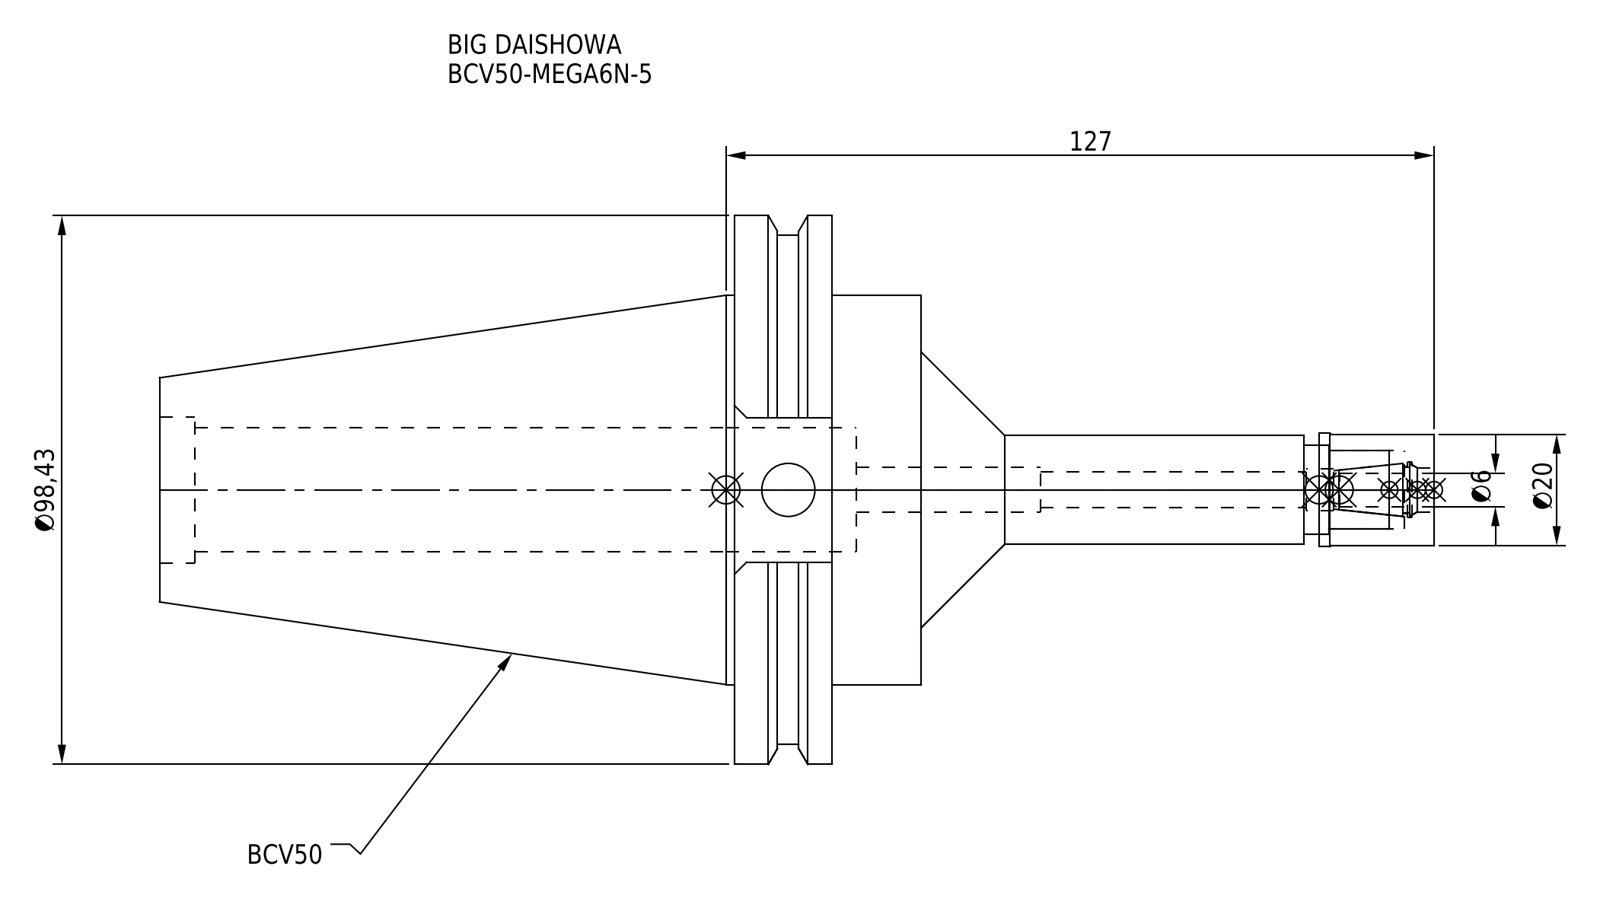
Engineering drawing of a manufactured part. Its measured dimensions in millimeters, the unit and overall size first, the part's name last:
Units: millimetres
Overall size (bounding box): 228.6 × 98.42 × 94.95
Round holes (diameter × count): ⌀6.4 ×1, ⌀7.5 ×1, ⌀7.9 ×1, ⌀8 ×1, ⌀8.5 ×1, ⌀9.53 ×1, ⌀10 ×1, ⌀14 ×1, ⌀16 ×1, ⌀22.3 ×1, ⌀26.23 ×1
Round bosses / shafts (diameter × count): ⌀98.42 ×1, ⌀91.29 ×1, ⌀69.85 ×1, ⌀20.3 ×1, ⌀20 ×1, ⌀19.5 ×1
Main face-to-face distances: 17.55, 15.95, 33.5, 136.6, 120.65, 103.1, 72.95, 11.6, 4.35, 21.9
Volume: 415 810 mm³ · Surface area: 58 369 mm²
Bodies: 2 solids, 91 faces (33 planar, 44 cylindrical, 14 other)
Part name (STEP PRODUCT): MGN6_1.stp; BCV50MN06050-060_ASM.stp; BCV50-MEGA6N-5-060-FreeParts; DXF_TEMP_ASSY_ASM_4_ASM.stp (+3 more)
STEP written by: SolidWorks 2019 (CONFIG_CONTROL_DESIGN)
